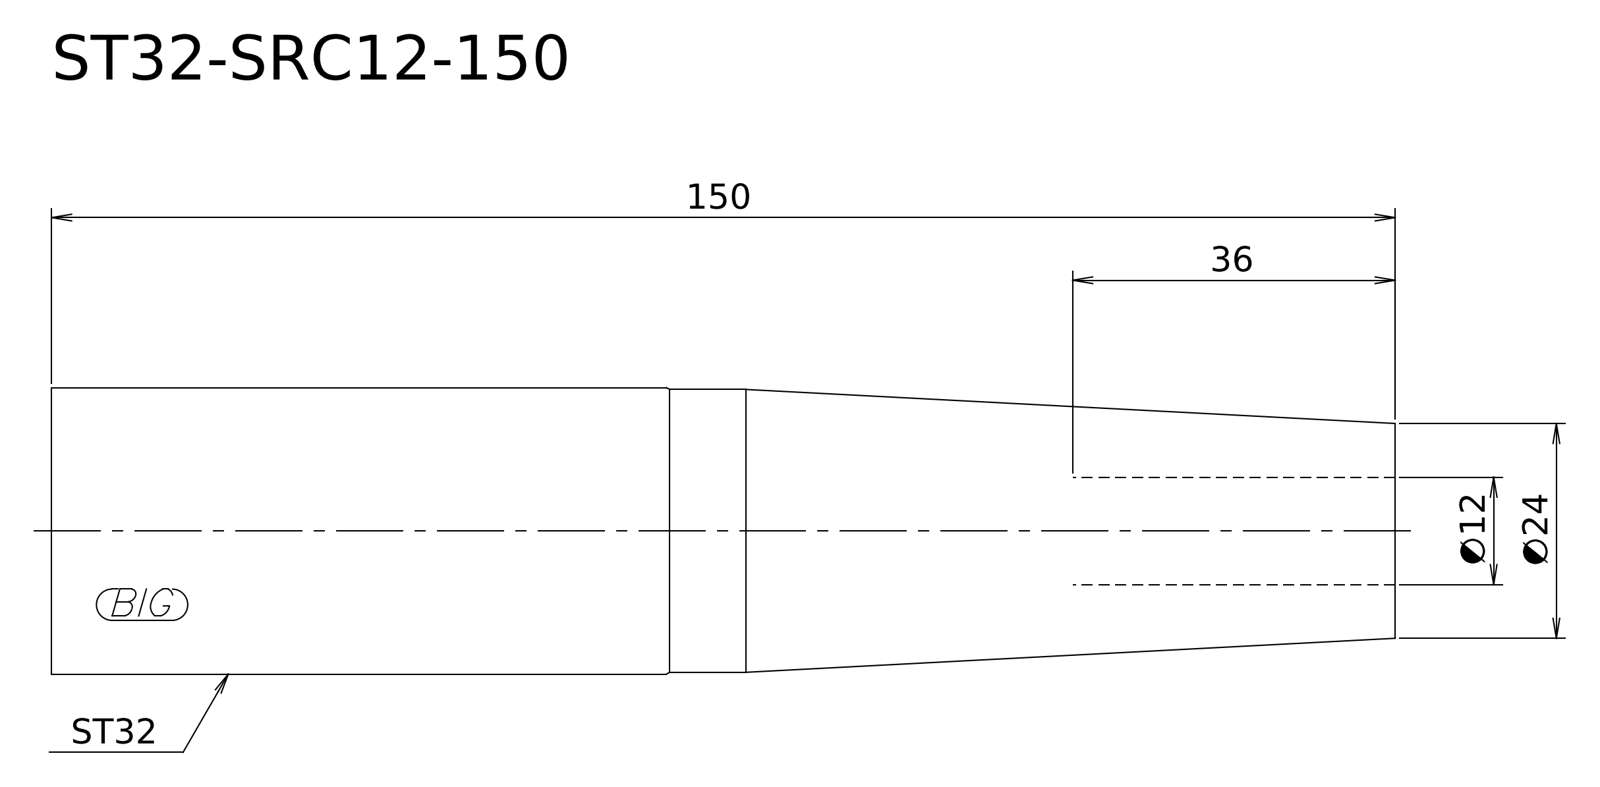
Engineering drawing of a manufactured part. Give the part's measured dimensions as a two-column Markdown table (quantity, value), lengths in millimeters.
| quantity | value |
| --- | --- |
| STEP written by | Kubotek KeyCreator V8.5.1 (14335) (CONFIG_CONTROL_DESIGN) |
| units | millimeters |
| bodies | 1 solid, 6 faces (2 planar, 2 cylindrical, 2 other) |
| overall size | 150 × 32 × 32 |
| volume | 106 435 mm³ |
| surface area | 15 383 mm² |
| round bosses / shafts (diameter × count) | 32 × 1, 31.6 × 1 |
| main face-to-face distances | 150 |
